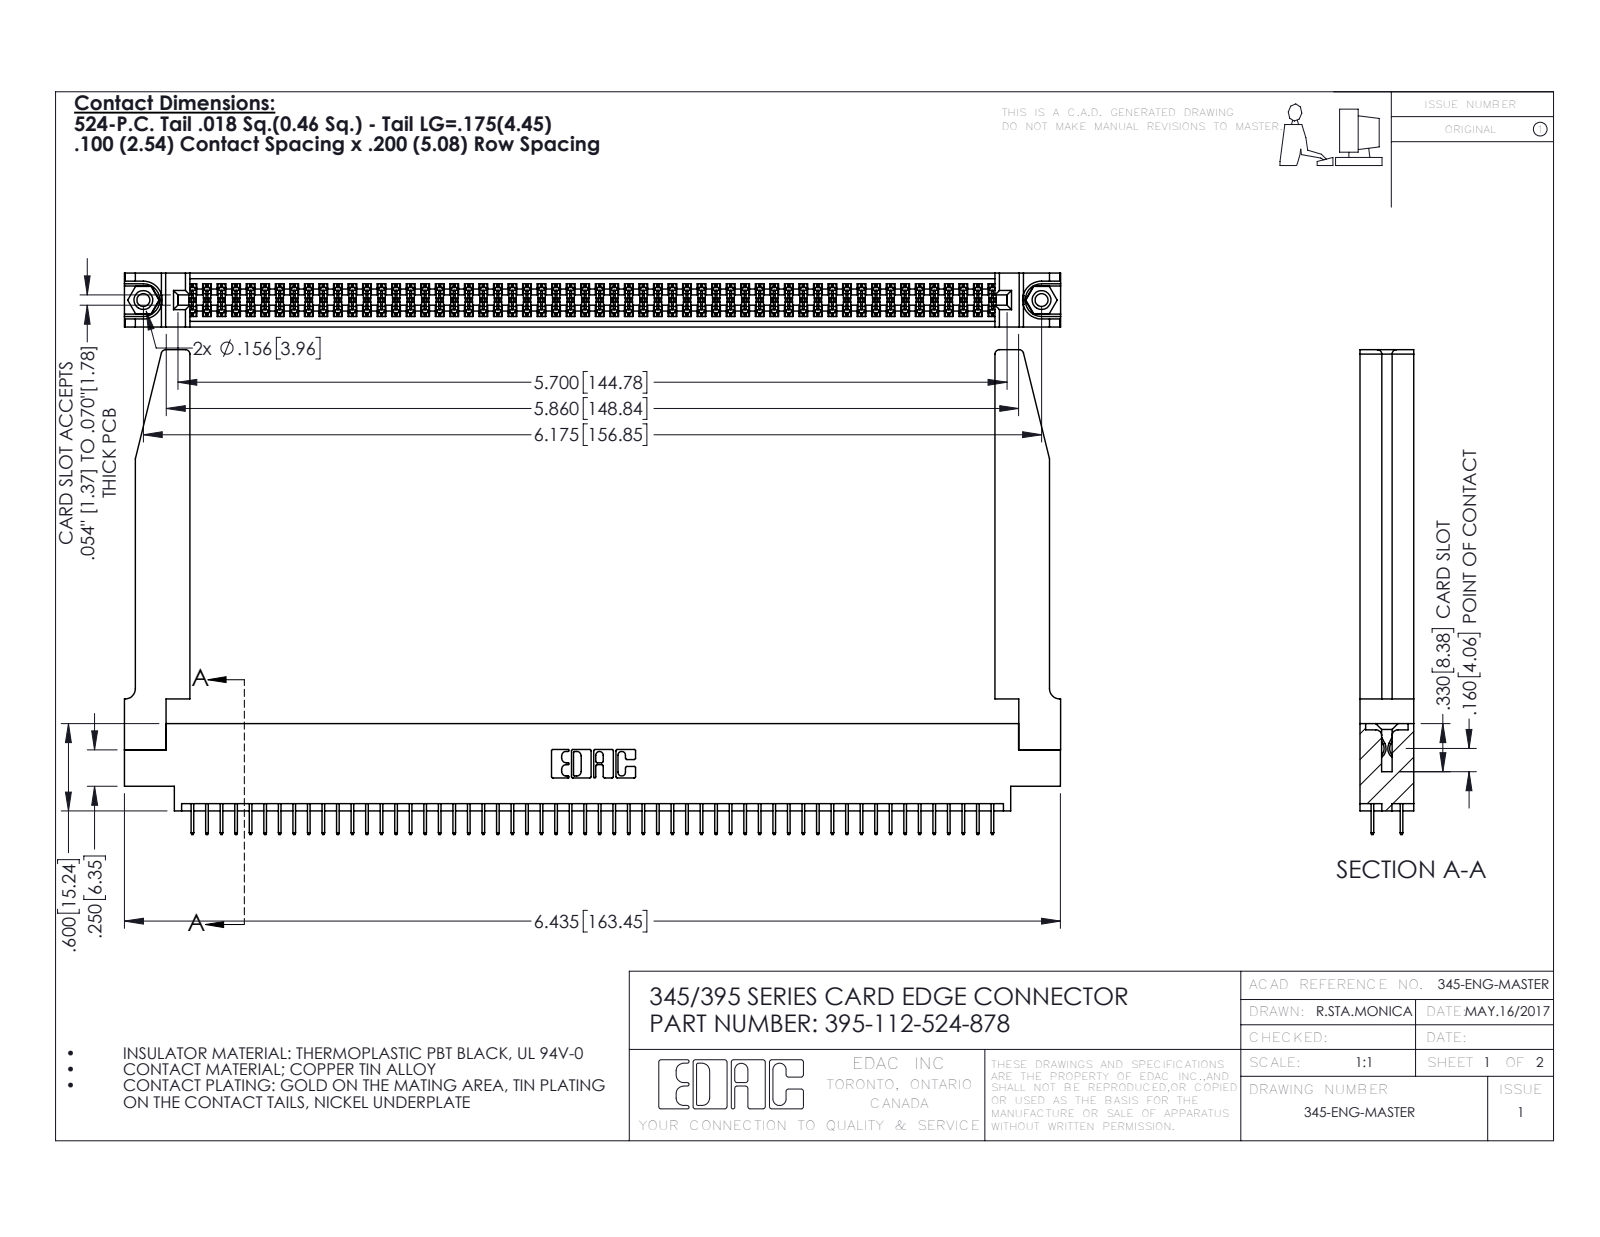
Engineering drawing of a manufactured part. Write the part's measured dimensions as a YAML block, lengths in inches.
part_name: "395-112-524-878; 345-292-001_345-293-124; 345 Part_0.170 Offset - 0.156 Dia-TH; 345-250-001_345-250-001-102 (+1 more)"
step_written_by: "SolidWorks 2016 (CONFIG_CONTROL_DESIGN)"
units: inches
bodies: {solids: 117, faces: 6412, planar: 4594, cylindrical: 1766, other: 52}
overall_size: [6.436, 3.332, 0.37]
volume: 1.434
surface_area: 46.58
round_holes:
  - {diameter: 0.089, count: 2}
  - {diameter: 0.125, count: 2}
  - {diameter: 0.156, count: 2}
  - {diameter: 0.064, count: 1}
round_bosses_or_shafts:
  - {diameter: 0.155, count: 2}
partial_cylinders:
  - {radius: 0.006, count: 168}
  - {radius: 0.01, count: 22}
  - {radius: 0.03, count: 8}
  - {radius: 0.007, count: 6}
  - {radius: 0.031, count: 6}
  - {radius: 0.026, count: 3}
  - {radius: 0.014, count: 2}
  - {radius: 0.019, count: 2}
face_to_face_distances: [0.37, 0.072, 0.298, 0.2, 0.098, 0.272, 0.025, 0.225, 0.072, 0.175]
hole_center_spacings: [0.27, 5.939, 6.175]
